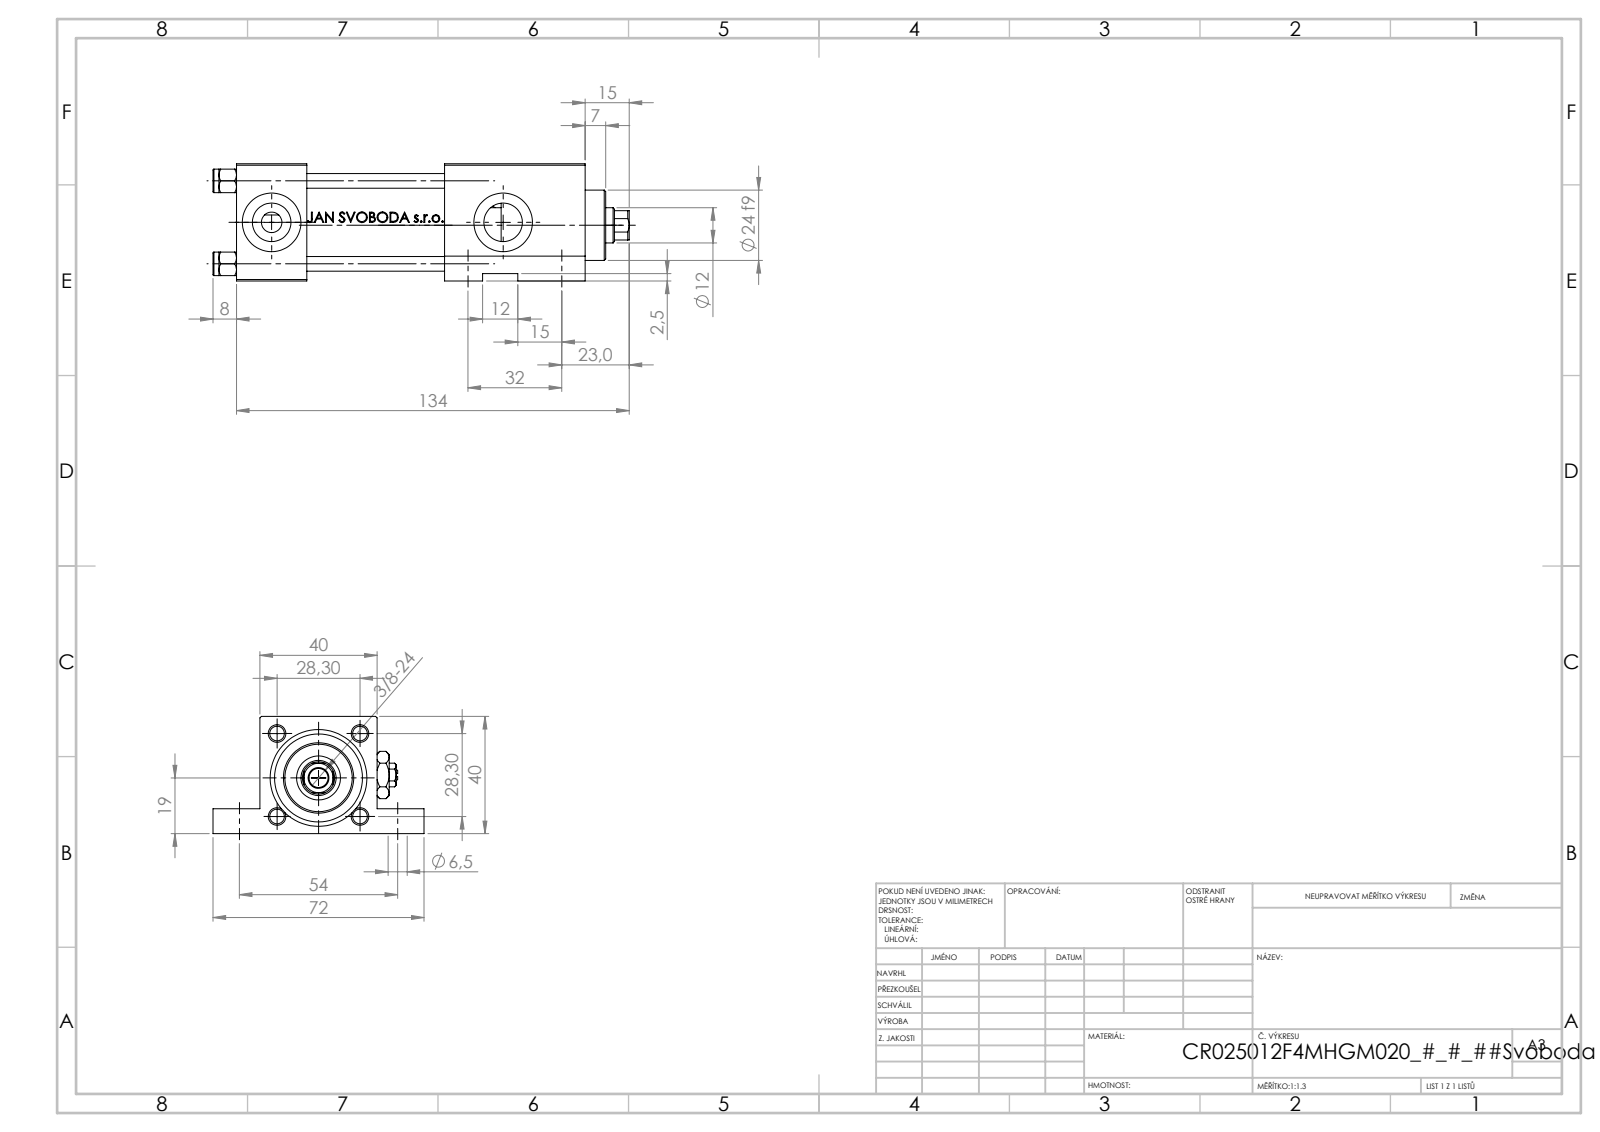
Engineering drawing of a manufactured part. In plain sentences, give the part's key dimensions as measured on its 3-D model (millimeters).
The part is named "V215CR_F_Body; Zatka_pro_OIL_PORT; NUT_M5_F; V215_VC_A (+2 more)". Its 3-D file was written by "SolidWorks 2019 (CONFIG_CONTROL_DESIGN)". It is 12 solids with 1150 faces: 460 planar, 130 cylindrical and 560 other. Overall it measures 142 by 72 by 40 millimeters. Its volume is 151 863 cubic millimeters and its surface area 59 189 square millimeters. Round holes: 5 of diameter 6.5, 4 of diameter 5, 4 of diameter 20, 3 of diameter 13.16, 2 of diameter 7, 1 of diameter 12, 1 of diameter 15, 1 of diameter 25, 1 of diameter 30. Round bosses or shafts: 4 of diameter 8, 1 of diameter 31, 1 of diameter 24. Partial cylindrical surfaces (rounded edges, fillets, slot ends): 1 of radius 5.5. The main face-to-face distances are 40, 24, 8.5, 31.5, 48, 47, 71, 119, 95, 6. The hole center spacings are 28.3, 19.32, 20.73, 32, 40.02, 54, 62.77, 7.
